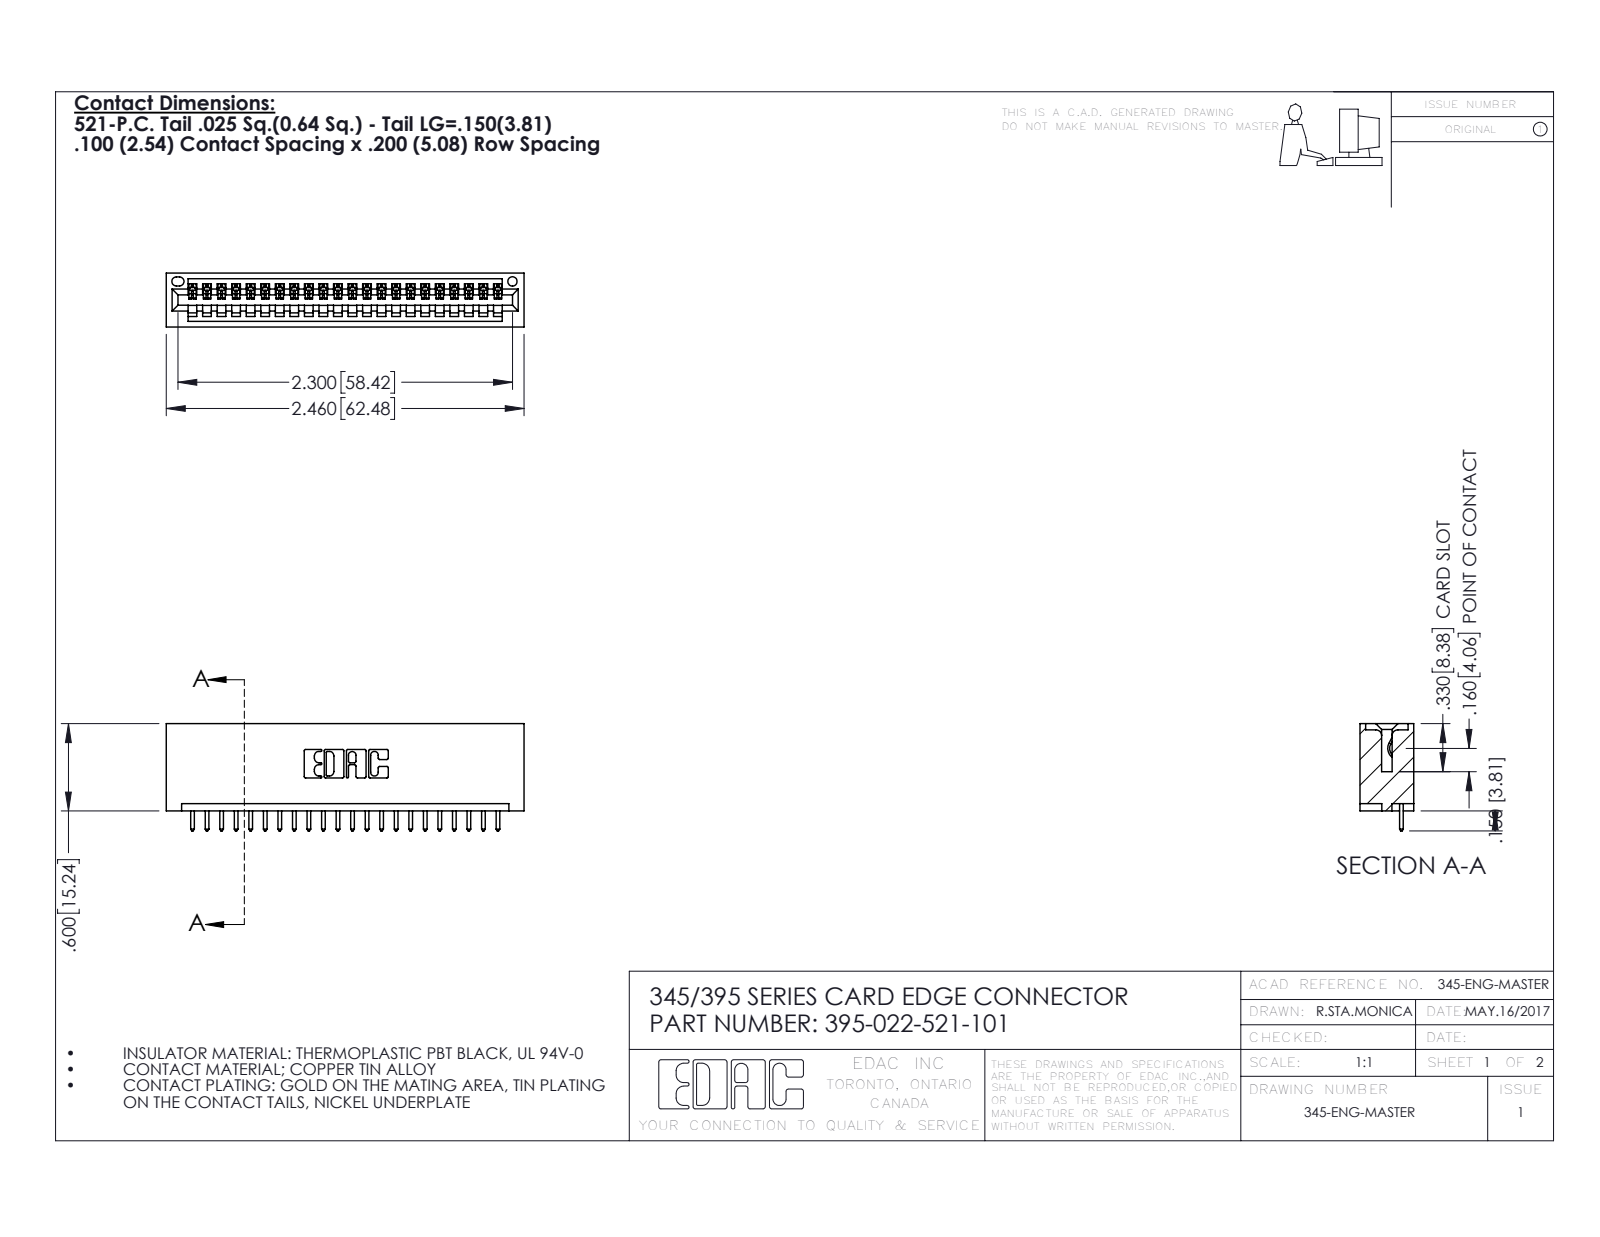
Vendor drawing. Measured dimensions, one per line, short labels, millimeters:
name: 345-292-001_345-293-121; 345 Part_No Mounting Lugs; 395-022-521-101
written by: SolidWorks 2016 (CONFIG_CONTROL_DESIGN)
unit: mm
bodies: 23 solids, 1394 faces (956 planar, 438 cylindrical, 0 other)
size: 62.5 × 18.7 × 9.4
volume: 6 290 mm³; area: 8 039 mm²
holes: 1× ⌀1.6
rounds: 44× R0.2, 44× R0.3, 22× R0.3, 6× R0.2, 6× R0.8, 3× R0.7, 2× R0.8, 2× R1
face distances: 7.6, 1.8, 5.1, 9.4, 2.5, 6.9, 0.6, 5.7, 2.5, 3.8
